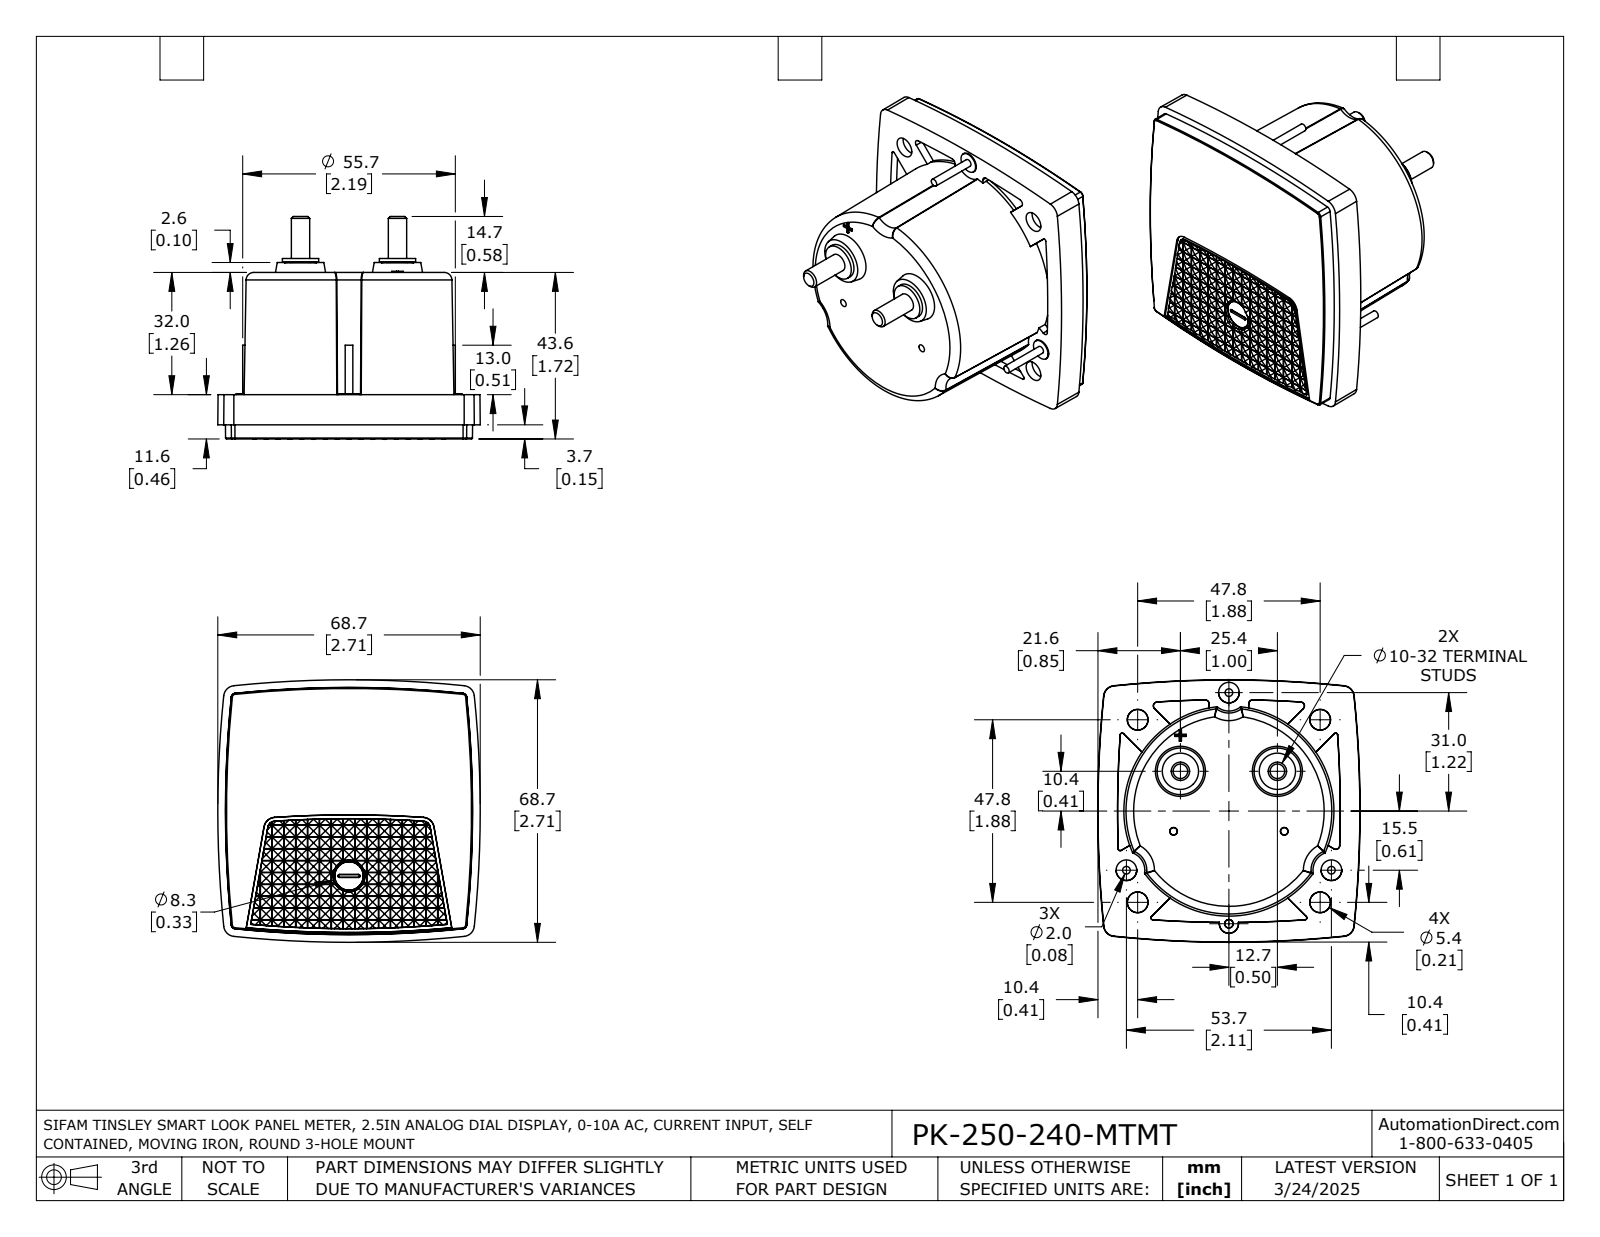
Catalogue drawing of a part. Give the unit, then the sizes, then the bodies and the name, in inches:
Units: inches
Overall size (bounding box): 2.706 × 2.706 × 2.297
Round bosses / shafts (diameter × count): ⌀0.213 ×3, ⌀0.079 ×3, ⌀0.374 ×2, ⌀0.189 ×2, ⌀0.215 ×1
Partial cylindrical surfaces — rounded edges, fillets, slot ends (radius × count): R0.167 ×2, R1.083 ×1
Main face-to-face distances: 1.717, 1.26, 0.457, 0.024, 0.087, 0.096, 0.311, 0.12, 0.072, 1.346
Volume: 7.594 in³ · Surface area: 30.41 in²
Bodies: 1 solid, 1550 faces (1165 planar, 265 cylindrical, 120 other)
Part name (STEP PRODUCT): PK-250-240-MTMT
STEP written by: SolidWorks 2021 (AUTOMOTIVE_DESIGN)
